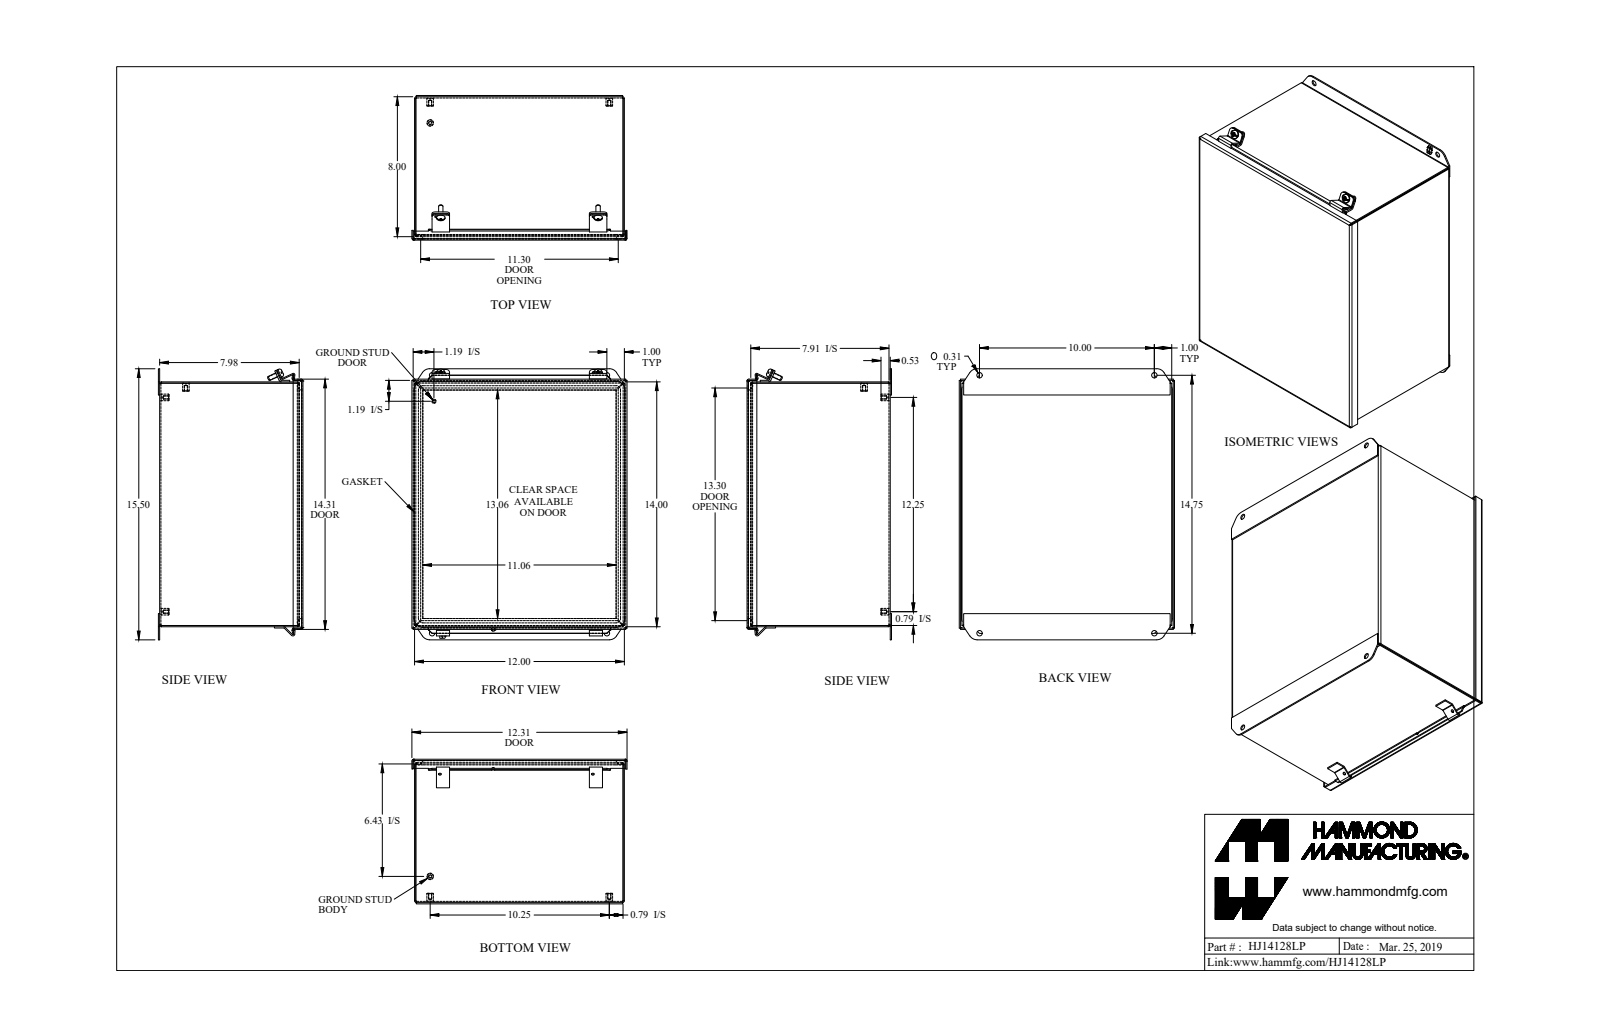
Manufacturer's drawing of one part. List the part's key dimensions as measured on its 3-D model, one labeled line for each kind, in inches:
Part name (STEP PRODUCT): HJ14128LP
STEP written by: SolidWorks 2018 (AUTOMOTIVE_DESIGN)
Units: inches
Bodies: 19 solids, 627 faces (341 planar, 160 cylindrical, 126 other)
Overall size (bounding box): 15.5 × 12.312 × 8.269
Volume: 65.21 in³ · Surface area: 1 807 in²
Round holes (diameter × count): ⌀0.156 ×5, ⌀0.313 ×4, ⌀0.156 ×2, ⌀0.213 ×2
Round bosses / shafts (diameter × count): ⌀0.375 ×5, ⌀0.25 ×3, ⌀0.48 ×2, ⌀0.188 ×1
Partial cylindrical surfaces — rounded edges, fillets, slot ends (radius × count): R0.036 ×16, R0.108 ×16, R0.25 ×16, R0.141 ×4, R0.188 ×4, R0.499 ×4, R0.5 ×4, R0.01 ×2
Main face-to-face distances: 0.072, 8.125, 11.928, 8.197, 13.928, 8.053, 11.856, 12, 14, 13.856
Hole centre spacings: 10, 10.25, 12.25, 15.972, 17.82, 1.239, 1.243, 1.27
